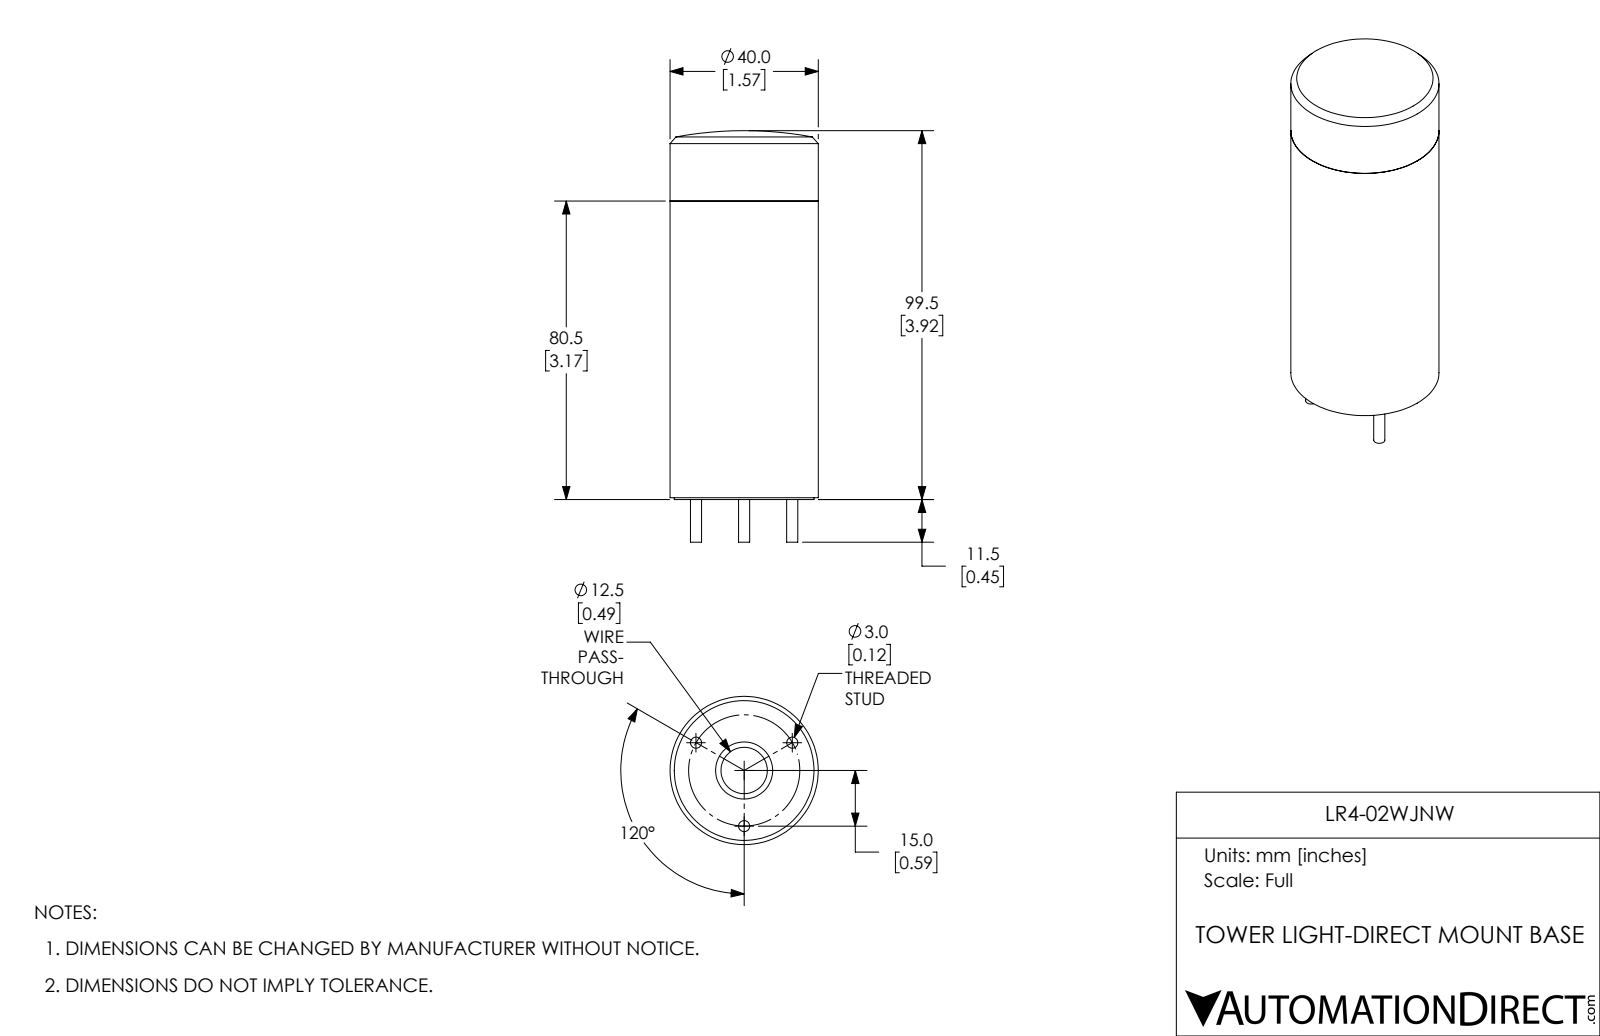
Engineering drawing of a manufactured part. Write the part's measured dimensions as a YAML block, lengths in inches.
part_name: "LR4-02WJNW"
step_written_by: "SolidWorks 2017 (AUTOMOTIVE_DESIGN)"
units: inches
bodies: {solids: 2, faces: 40, planar: 13, cylindrical: 24, other: 3}
overall_size: [4.369, 1.575, 1.575]
volume: 7.514
surface_area: 31.02
round_holes:
  - {diameter: 0.492, count: 1}
  - {diameter: 0.606, count: 1}
  - {diameter: 1.366, count: 1}
  - {diameter: 1.461, count: 1}
round_bosses_or_shafts:
  - {diameter: 0.118, count: 3}
  - {diameter: 1.575, count: 1}
  - {diameter: 1.484, count: 1}
face_to_face_distances: [3.575, 3.169, 0.406, 3.295, 0.126, 0.28, 0.02, 3.15, 3.276, 3.555]
